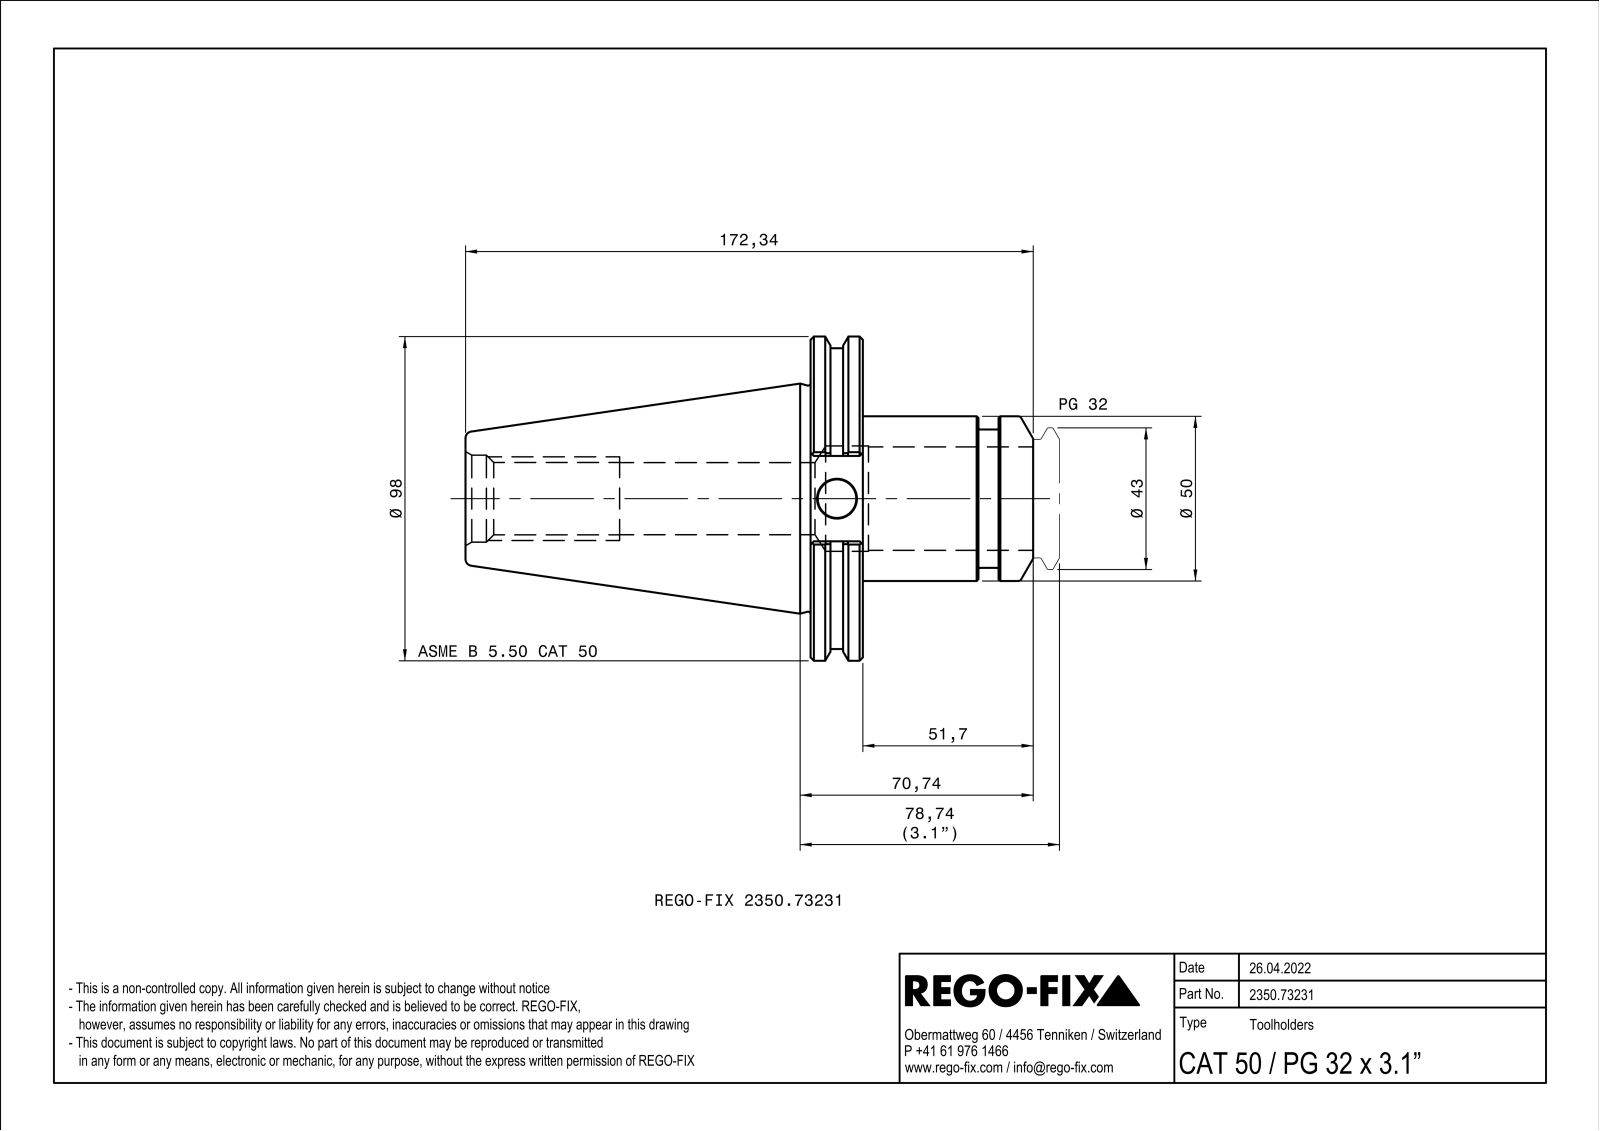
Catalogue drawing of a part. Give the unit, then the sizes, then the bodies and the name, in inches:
Units: inches
Overall size (bounding box): 6.785 × 3.875 × 3.717
Round holes (diameter × count): ⌀0.461 ×1, ⌀0.862 ×1, ⌀0.865 ×1, ⌀1.031 ×1, ⌀1.299 ×1
Round bosses / shafts (diameter × count): ⌀3.875 ×1, ⌀3.594 ×1, ⌀1.969 ×1, ⌀1.957 ×1, ⌀1.654 ×1, ⌀1.02 ×1
Partial cylindrical surfaces — rounded edges, fillets, slot ends (radius × count): R0.02 ×12
Main face-to-face distances: 0.625, 1.381, 2.007, 0.24, 1.622, 2.247, 6.371, 6.131, 4.75, 4.124
Volume: 22.37 in³ · Surface area: 89.52 in²
Bodies: 1 solid, 96 faces (34 planar, 29 cylindrical, 33 other)
Part name (STEP PRODUCT): NOCUT
STEP written by: SIEMENS PLM Software Solid Edge ST10 (AUTOMOTIVE_DESIGN)
